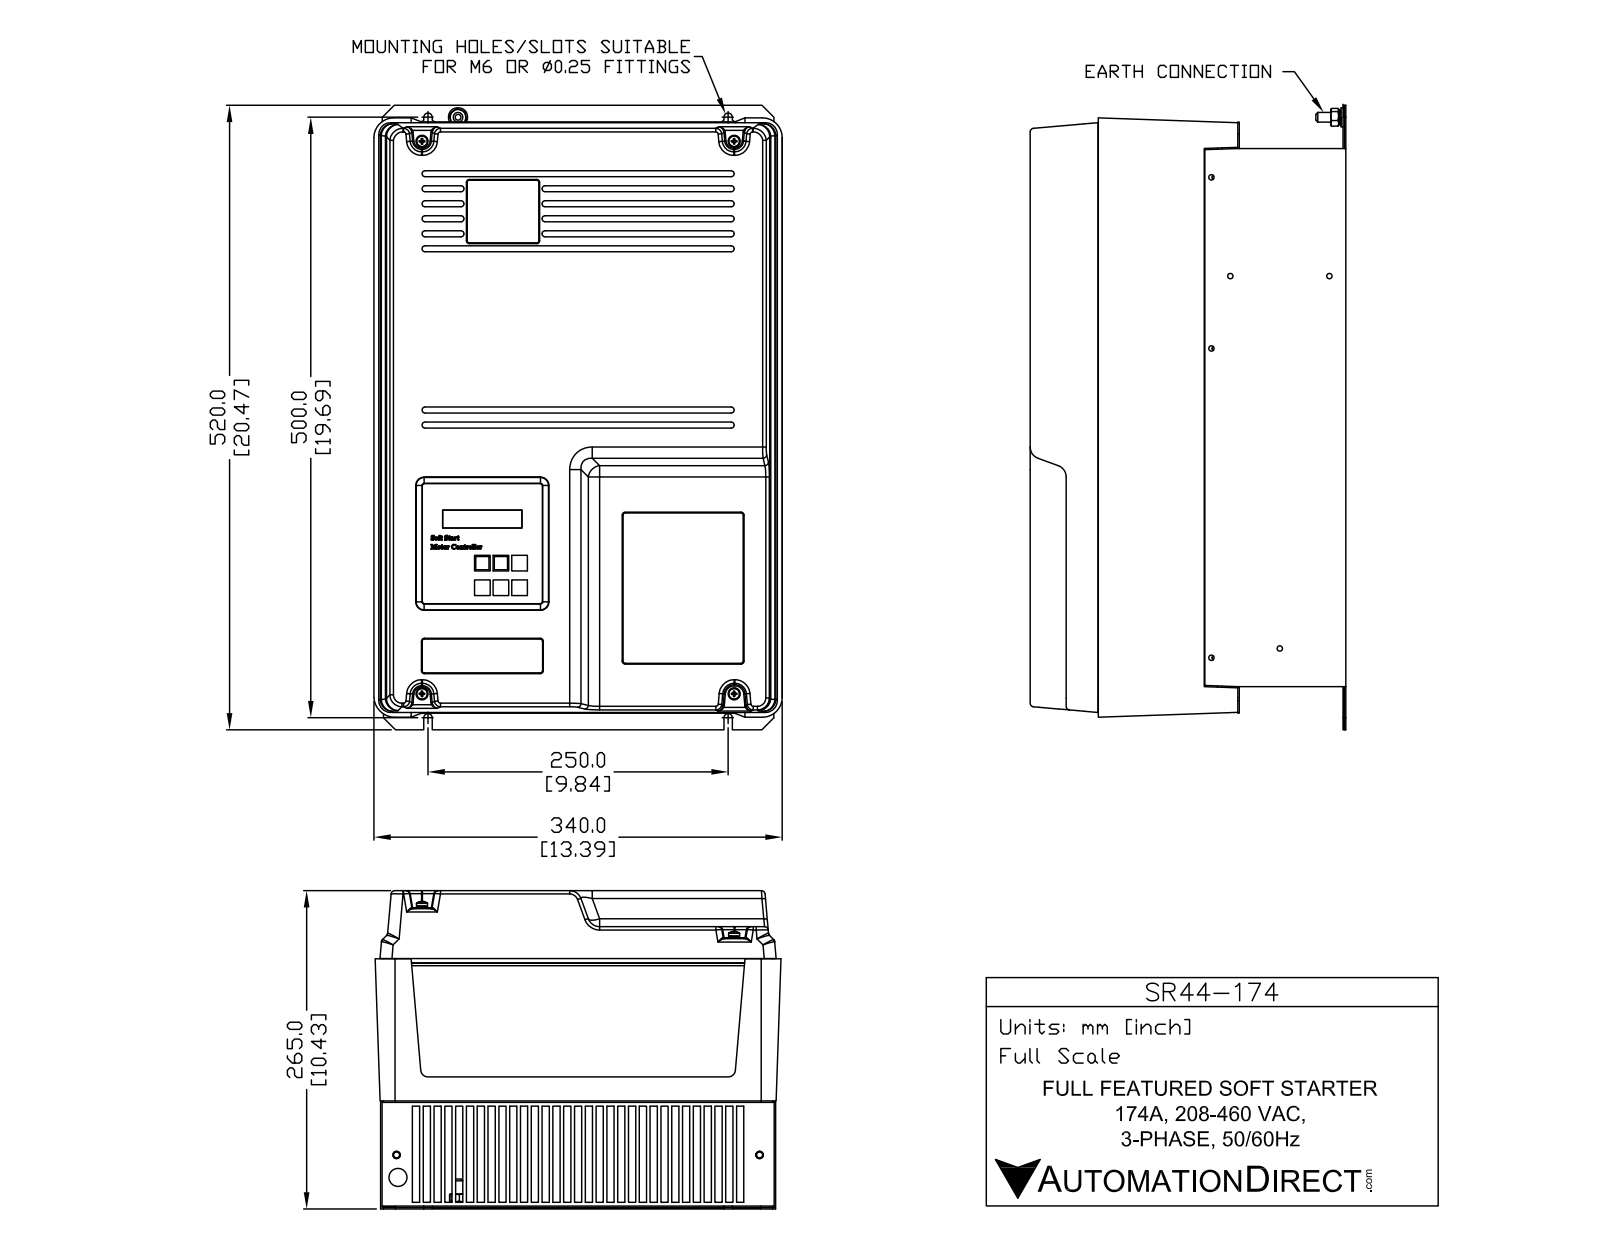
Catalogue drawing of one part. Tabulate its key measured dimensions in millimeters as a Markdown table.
| quantity | value |
| --- | --- |
| part name | SR44-174 |
| STEP written by | SolidWorks 2013 (AUTOMOTIVE_DESIGN) |
| units | millimeters |
| bodies | 1 solid, 828 faces (518 planar, 144 cylindrical, 166 other) |
| overall size | 520 × 337.91 × 263 |
| volume | 38 650 000 mm³ |
| surface area | 1 324 000 mm² |
| round holes (diameter × count) | 13 × 2 |
| round bosses / shafts (diameter × count) | 10 × 4, 16 × 1, 8 × 1 |
| partial cylindrical surfaces (radius × count) | 5 × 31, 3 × 16, 2.4 × 12, 1.5 × 8, 15 × 8, 2 × 6, 3.5 × 4, 10 × 2 |
| main face-to-face distances | 8.9, 17.8, 26.7, 35.6, 263, 5.75, 14.65, 44.5, 3.15, 23.55 |
| hole center spacings | 250 |
